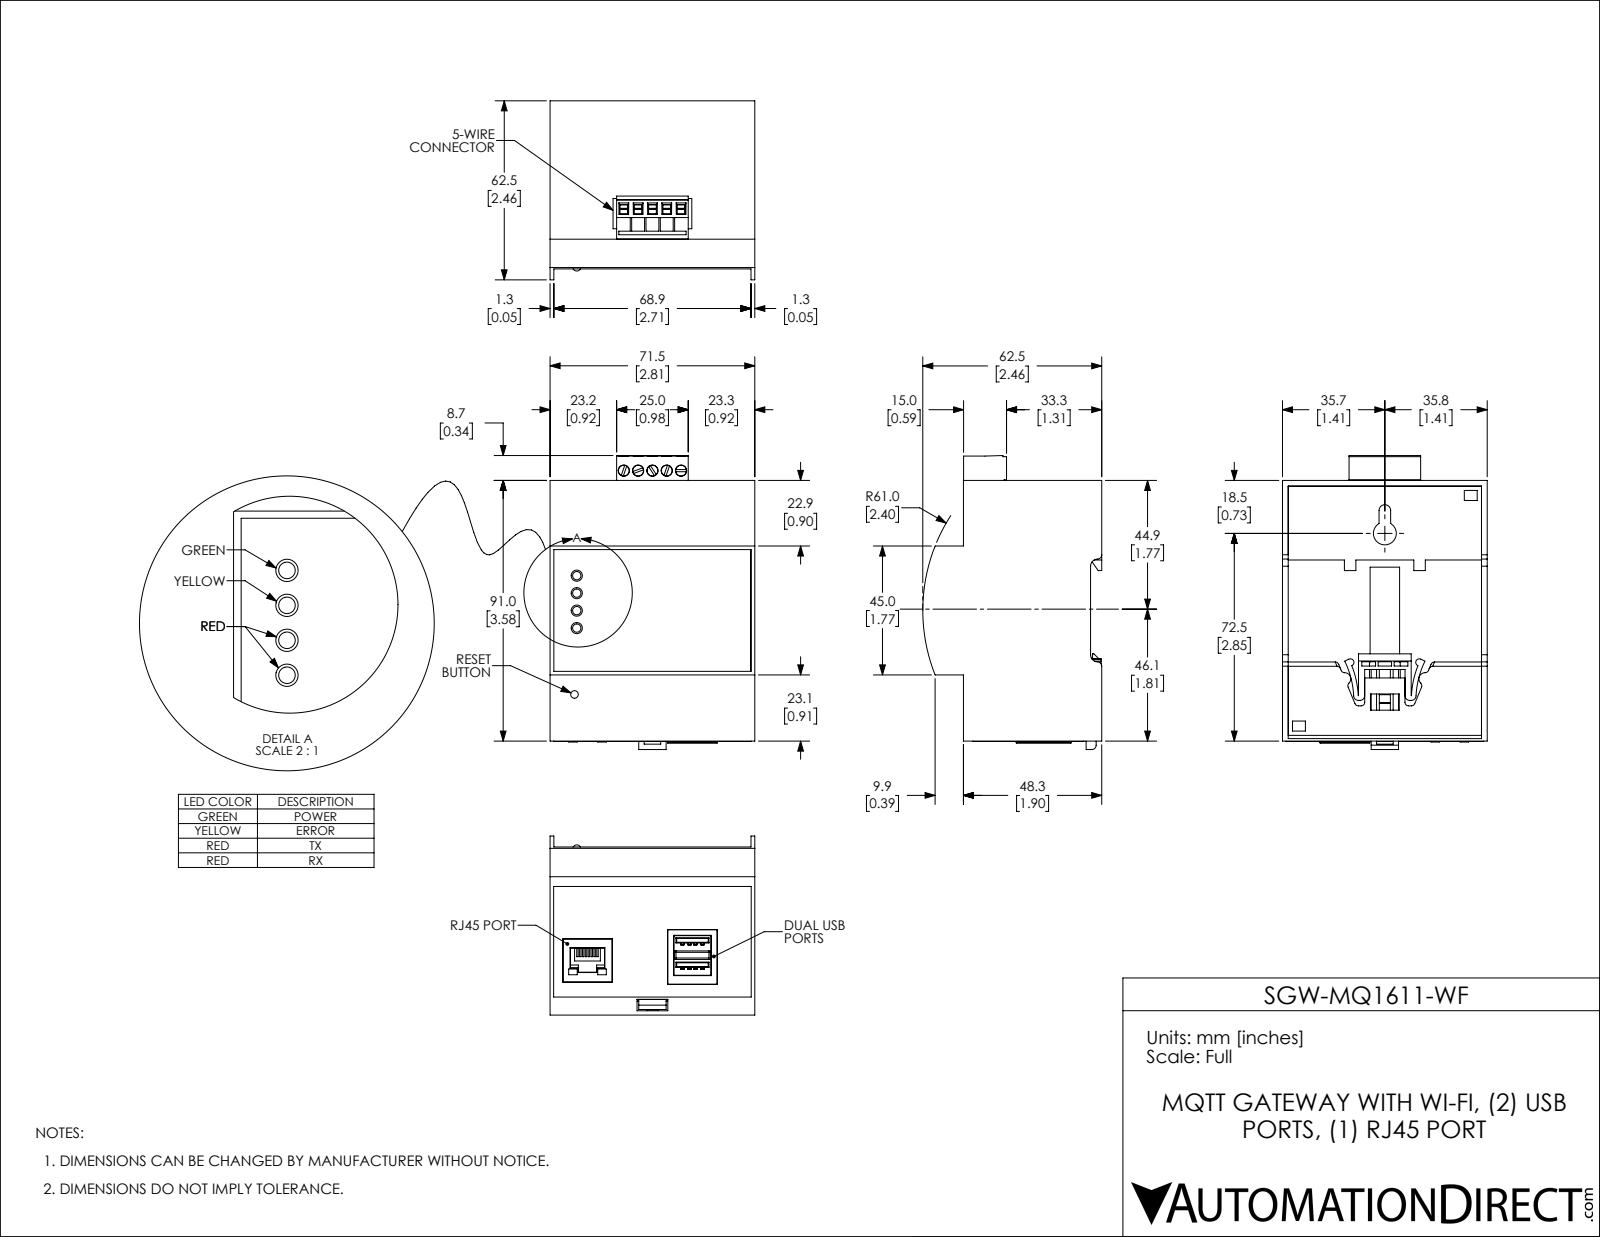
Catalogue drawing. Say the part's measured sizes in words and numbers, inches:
The part is named "SS10680". Its 3-D file was written by "SolidWorks 2018 (AUTOMOTIVE_DESIGN)". It is 19 solids with 797 faces: 635 planar, 145 cylindrical and 17 other. Overall it measures 4.04 by 2.815 by 2.461 inches. Its volume is 5.303 cubic inches and its surface area 133.9 square inches. Round holes: 5 of diameter 0.063, 5 of diameter 0.124, 5 of diameter 0.154, 4 of diameter 0.154, 1 of diameter 0.104, 1 of diameter 0.315. Round bosses or shafts: 5 of diameter 0.148, 5 of diameter 0.114. Partial cylindrical surfaces (rounded edges, fillets, slot ends): 15 of radius 0.005, 10 of radius 0.05, 8 of radius 0.008, 6 of radius 0.02, 4 of radius 0.065, 3 of radius 0.01, 2 of radius 0.004, 2 of radius 0.049. The main face-to-face distances are 0.079, 2.736, 1.969, 0.39, 3.504, 1.823, 0.084, 1.579, 2.213, 2.815. The hole center spacings are 0.197, 0.394, 0.591, 0.24, 0.48, 0.787, 0.885, 0.948.
